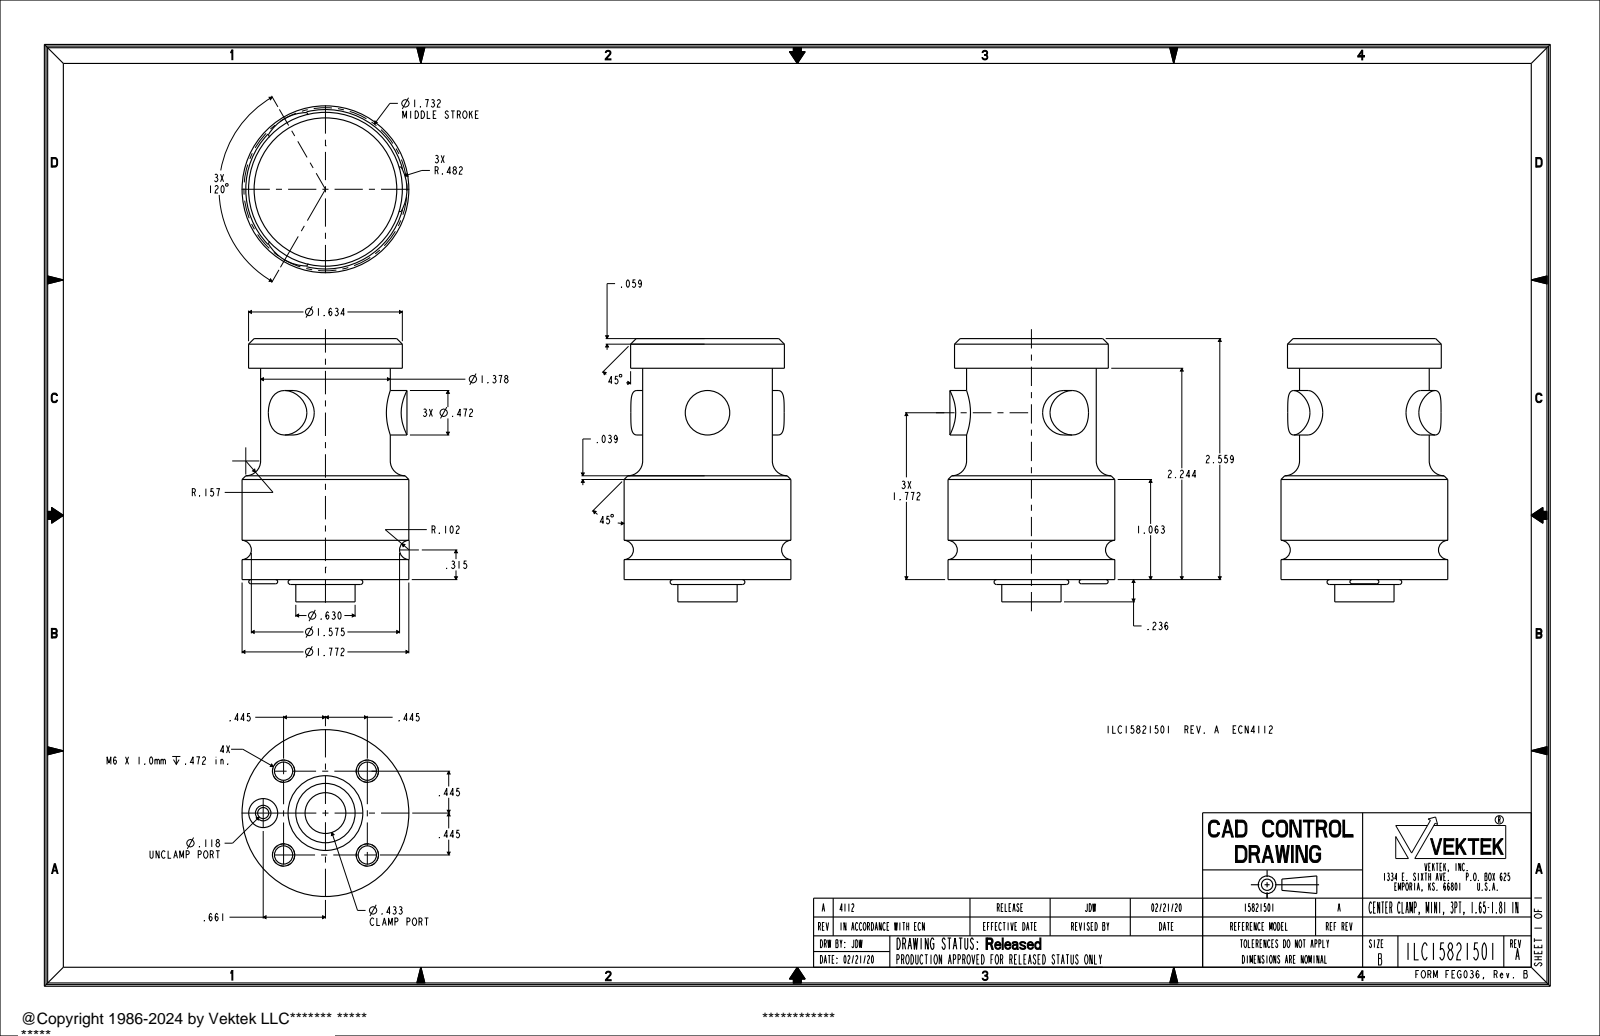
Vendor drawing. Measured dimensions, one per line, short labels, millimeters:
name: ILC15821501
written by: PRO/ENGINEER BY PARAMETRIC TECHNOLOGY CORPORATION, 2013320 (AUTOMOTIVE_DESIGN)
unit: mm
bodies: 1 solid, 89 faces (18 planar, 39 cylindrical, 32 other)
size: 71 × 45 × 45
volume: 83 340 mm³; area: 15 270 mm²
holes: 4× ⌀4.9, 1× ⌀3, 1× ⌀11
bosses: 4× ⌀6, 3× ⌀12, 1× ⌀45, 1× ⌀41.5, 1× ⌀35, 1× ⌀16
rounds: 3× R12.2
face distances: 65, 8, 57, 63, 6, 71, 5, 1, 58, 66
hole spacings: 16, 22.6, 12.6, 30.3, 32, 16.8
